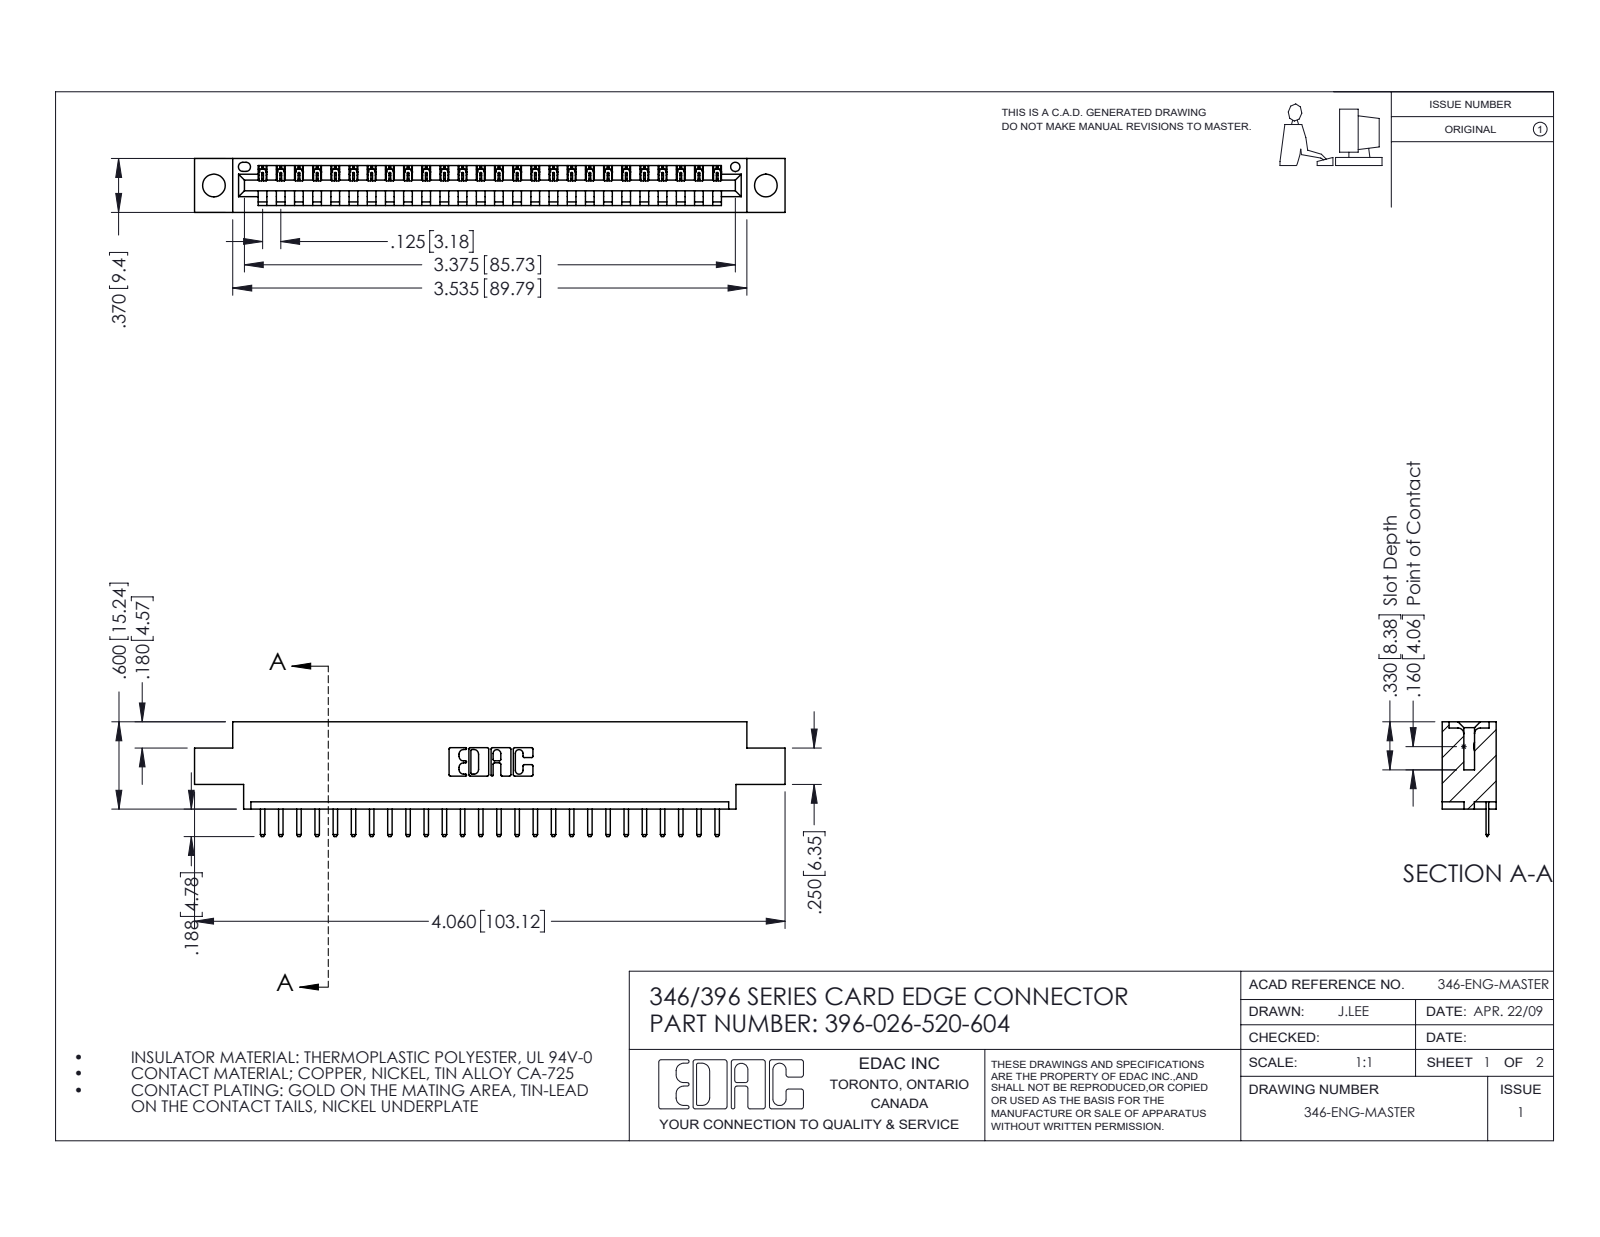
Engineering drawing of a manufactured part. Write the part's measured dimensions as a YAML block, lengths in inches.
part_name: "346 Part_0.170 Offset - 0.156 Dia-TH; 396-026-520-604; 345-292-001_345-293-120"
step_written_by: "SolidWorks 2016 (CONFIG_CONTROL_DESIGN)"
units: inches
bodies: {solids: 27, faces: 1738, planar: 1172, cylindrical: 566, other: 0}
overall_size: [4.06, 0.788, 0.37]
volume: 0.576
surface_area: 17.59
round_holes:
  - {diameter: 0.156, count: 2}
  - {diameter: 0.064, count: 1}
partial_cylinders:
  - {radius: 0.01, count: 54}
  - {radius: 0.006, count: 52}
  - {radius: 0.01, count: 22}
  - {radius: 0.007, count: 6}
  - {radius: 0.031, count: 6}
  - {radius: 0.026, count: 3}
  - {radius: 0.031, count: 2}
  - {radius: 0.04, count: 2}
face_to_face_distances: [0.048, 0.322, 0.37, 0.25, 0.148, 0.222, 0.1, 0.174, 0.072, 0.298]
hole_center_spacings: [0.246, 3.587, 3.795]
